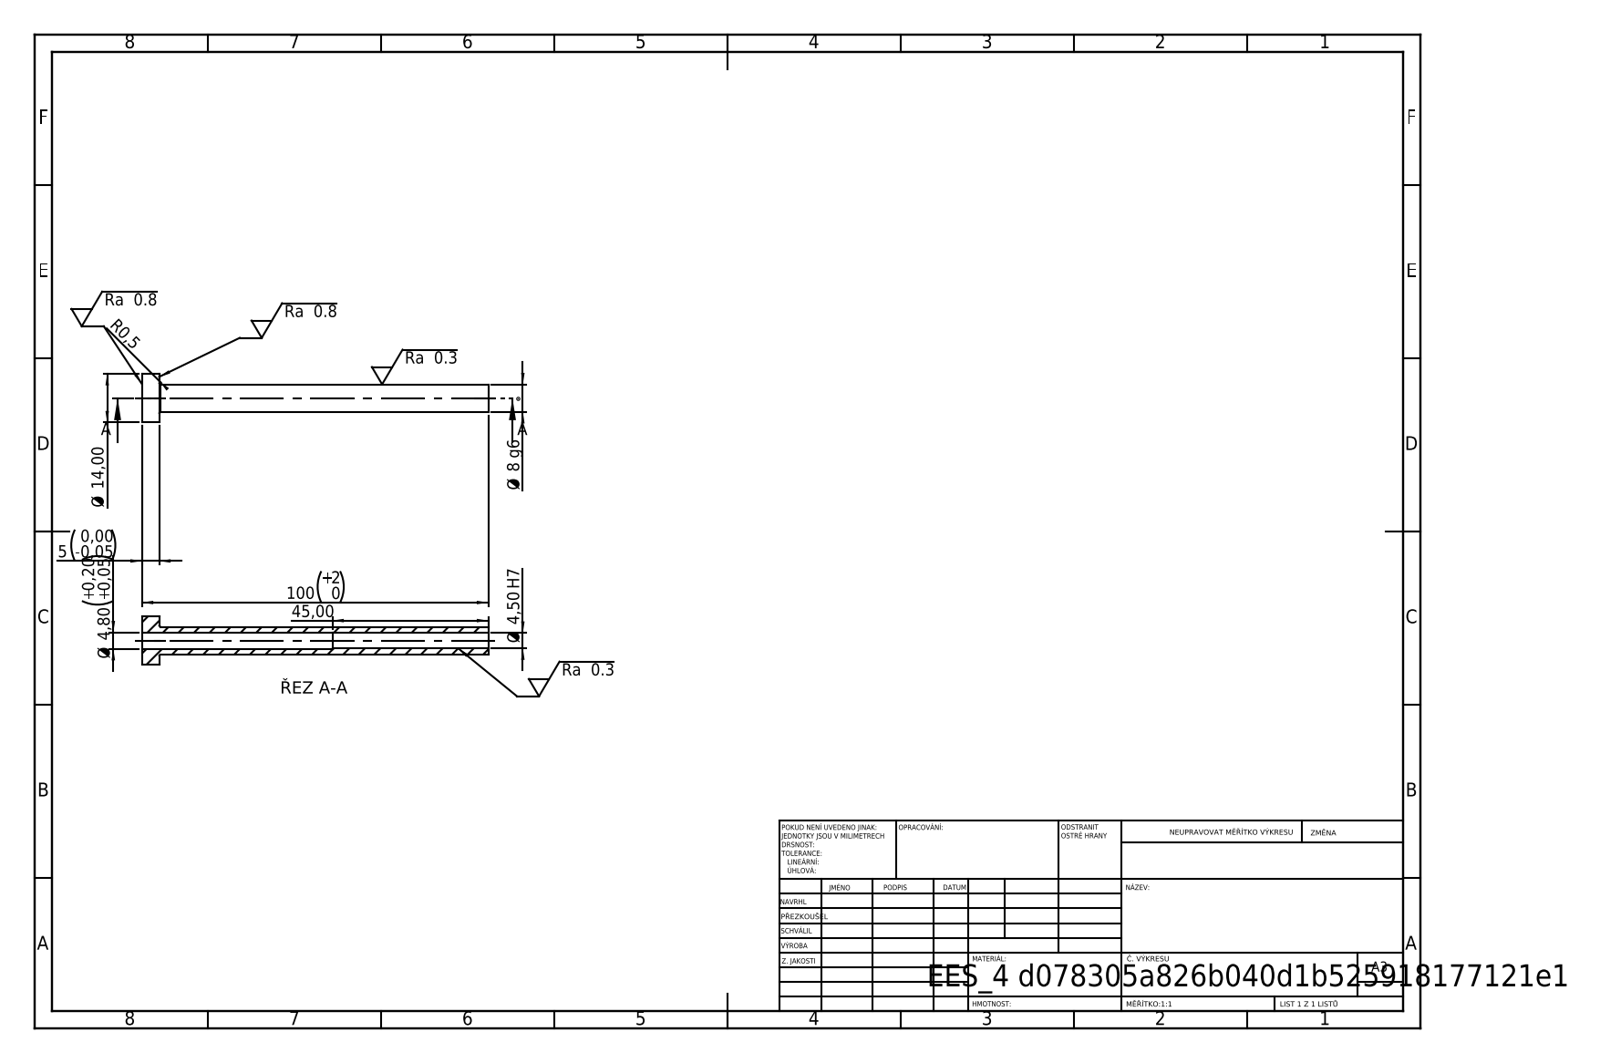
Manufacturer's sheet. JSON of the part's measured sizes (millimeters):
{"step_written_by": "SolidWorks 2019 (CONFIG_CONTROL_DESIGN)", "units": "millimeters", "bodies": {"solids": 1, "faces": 14, "planar": 4, "cylindrical": 8, "other": 2}, "overall_size": [100, 14, 14], "volume_mm3": 3835, "surface_area_mm2": 4344, "round_holes": [[4.5, 1], [4.8, 1]], "round_bosses_or_shafts": [[14, 1], [8, 1]], "face_to_face_distances": [5, 100, 95, 55, 50, 45]}
